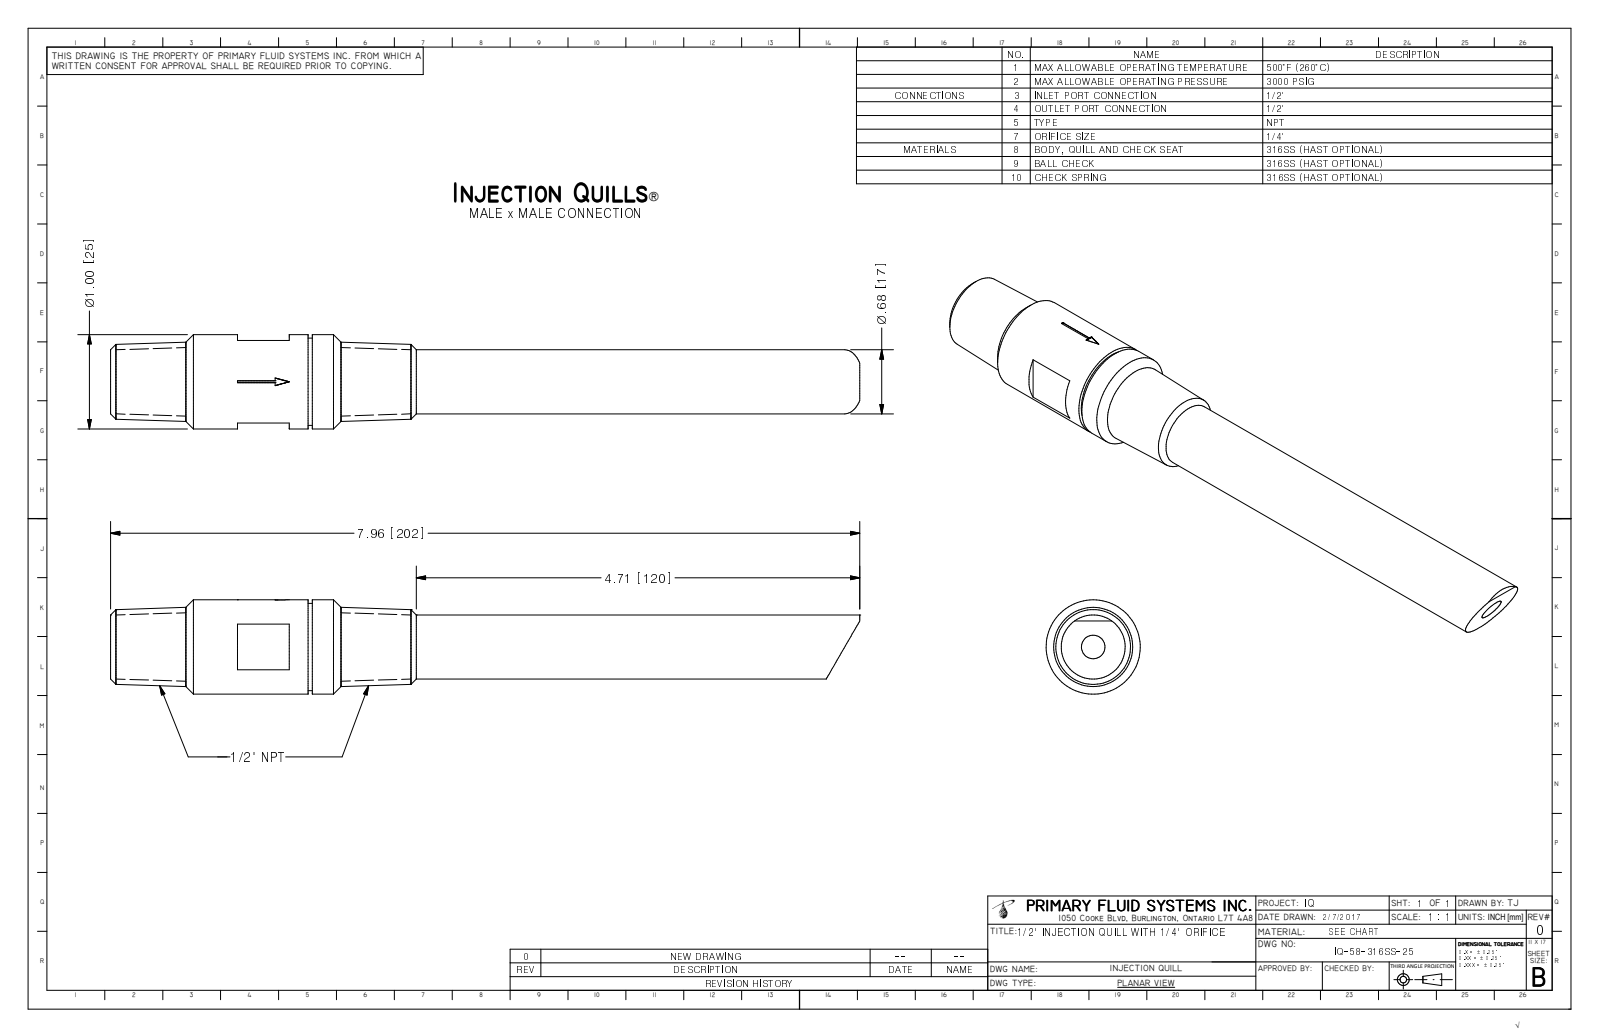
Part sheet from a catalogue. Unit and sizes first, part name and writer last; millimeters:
Units: millimetres
Overall size (bounding box): 202.3 × 25.4 × 25.4
Round holes (diameter × count): ⌀6.4 ×1, ⌀11.9 ×1
Round bosses / shafts (diameter × count): ⌀25.4 ×1, ⌀23.5 ×1, ⌀17.2 ×1
Partial cylindrical surfaces — rounded edges, fillets, slot ends (radius × count): R12.7 ×1
Main face-to-face distances: 22.2, 19.1, 34.3, 53.3, 54.5, 35.4, 1.1, 3.8, 57.2, 38.1
Volume: 54 490 mm³ · Surface area: 16 610 mm²
Bodies: 1 solid, 33 faces (18 planar, 7 cylindrical, 8 other)
Part name (STEP PRODUCT): IQ-58-316SS-25_R0
STEP written by: Autodesk Inventor 2009 (AUTOMOTIVE_DESIGN)
